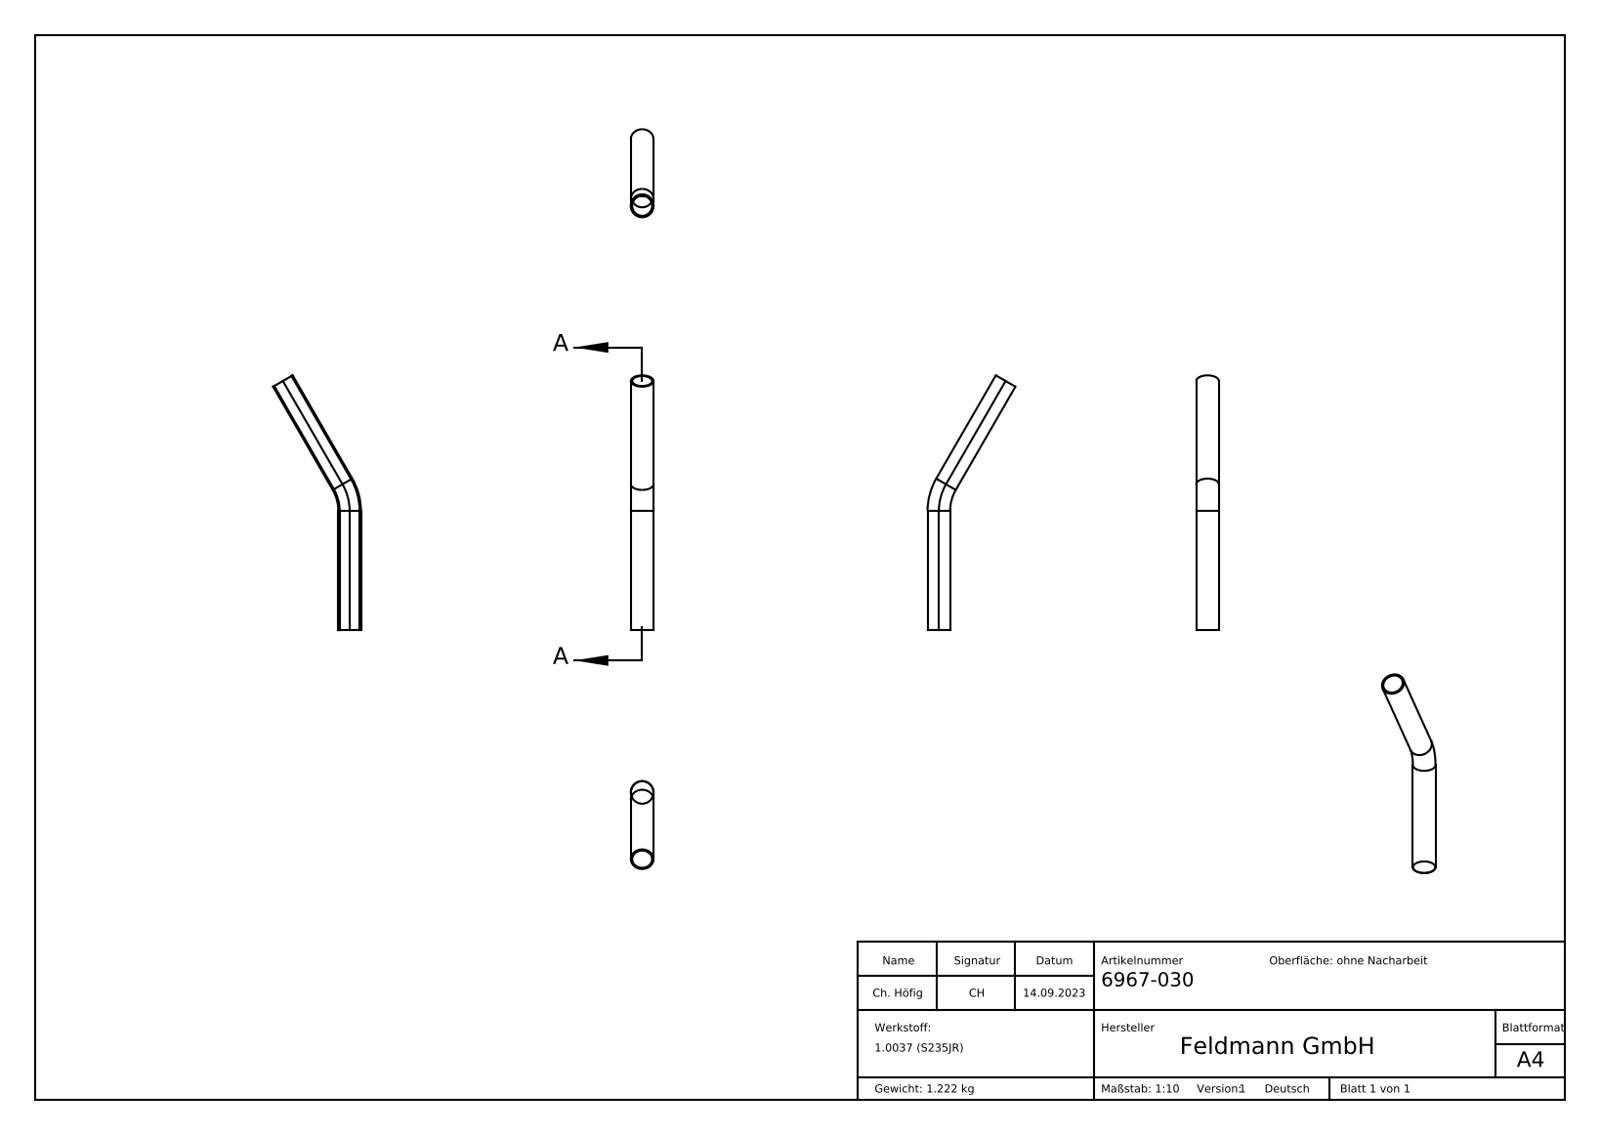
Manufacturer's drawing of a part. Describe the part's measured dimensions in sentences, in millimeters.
The part is named "6967-030". Its 3-D file was written by "SolidWorks 2018 (CONFIG_CONTROL_DESIGN)". It is 1 solid with 215 faces: 102 planar, 4 cylindrical and 109 other. Overall it measures 478.25 by 164.87 by 42.4 millimeters. Its volume is 156 687 cubic millimeters and its surface area 125 980 square millimeters. Round holes: 2 of diameter 37.4. Round bosses or shafts: 2 of diameter 42.4. The main face-to-face distances are 0.54, 0.49, 0.34, 0.53, 0.58, 0.31, 0.39, 0.48, 0.32.
